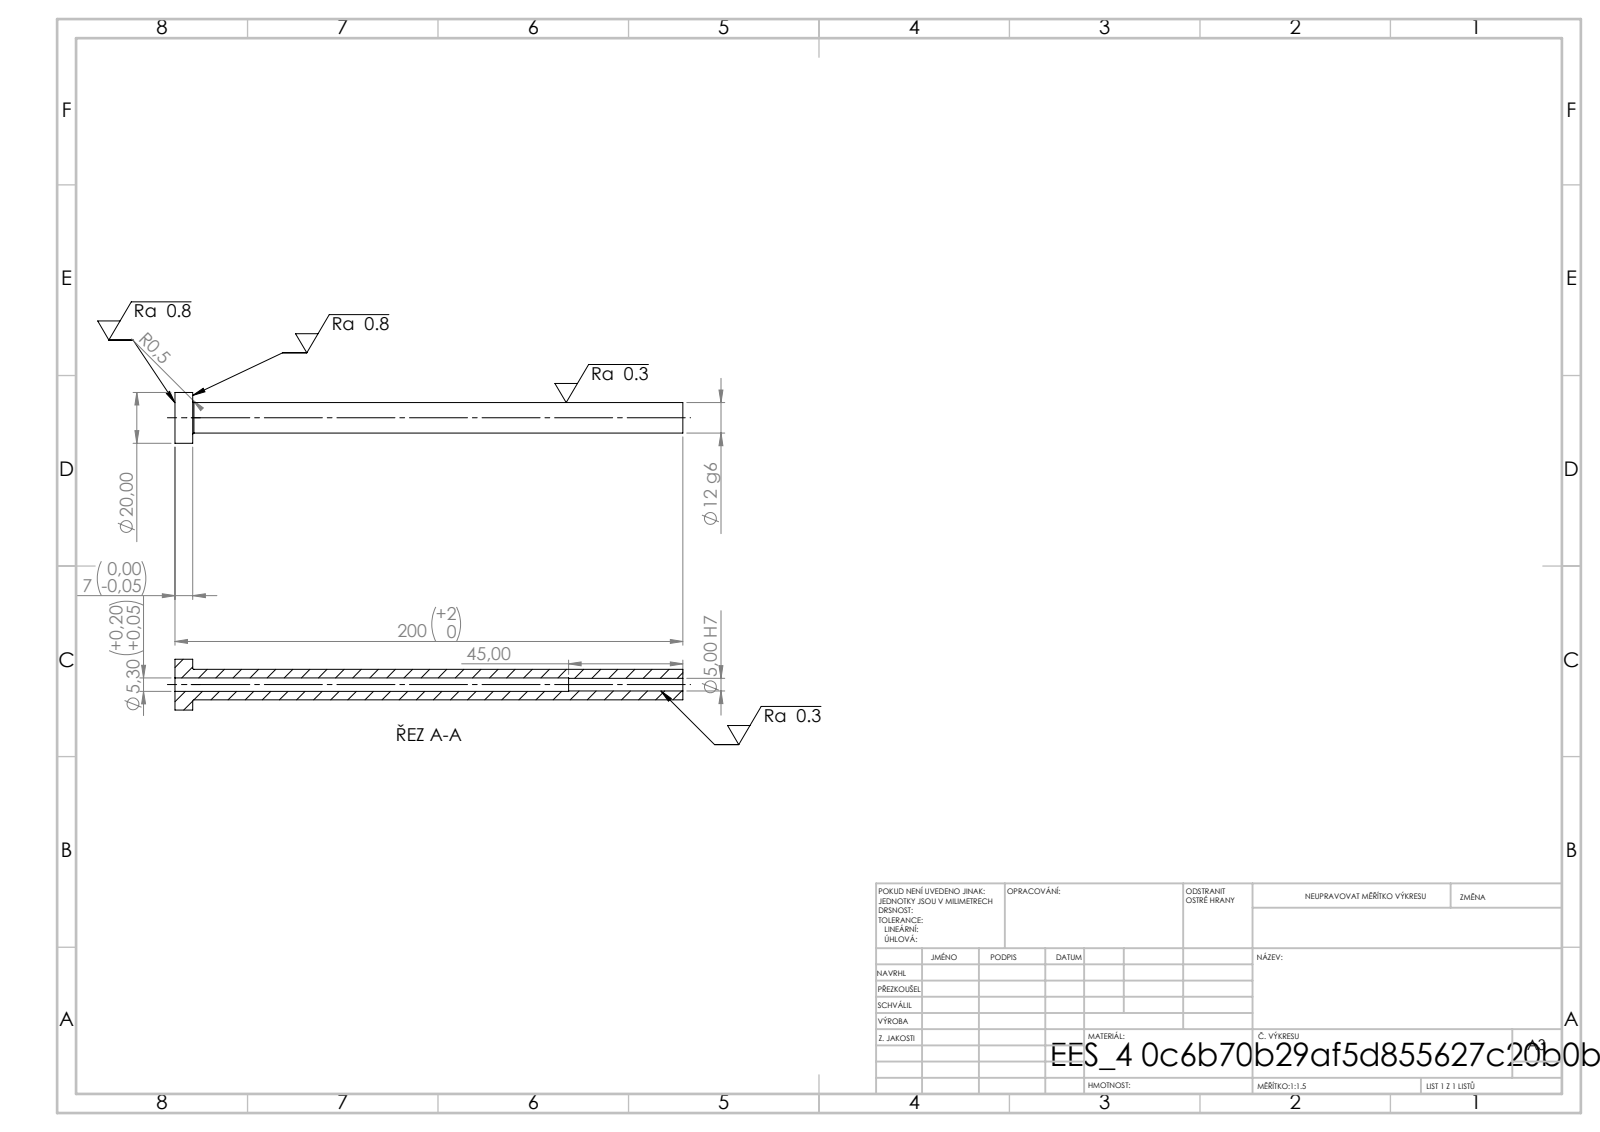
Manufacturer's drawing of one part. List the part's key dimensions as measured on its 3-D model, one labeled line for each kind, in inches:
STEP written by: SolidWorks 2019 (CONFIG_CONTROL_DESIGN)
Units: inches
Bodies: 1 solid, 14 faces (4 planar, 8 cylindrical, 2 other)
Overall size (bounding box): 7.874 × 0.787 × 0.787
Volume: 1.204 in³ · Surface area: 17.96 in²
Round holes (diameter × count): ⌀0.197 ×1, ⌀0.209 ×1
Round bosses / shafts (diameter × count): ⌀0.787 ×1, ⌀0.472 ×1
Main face-to-face distances: 0.276, 7.874, 7.598, 6.102, 5.827, 1.772
